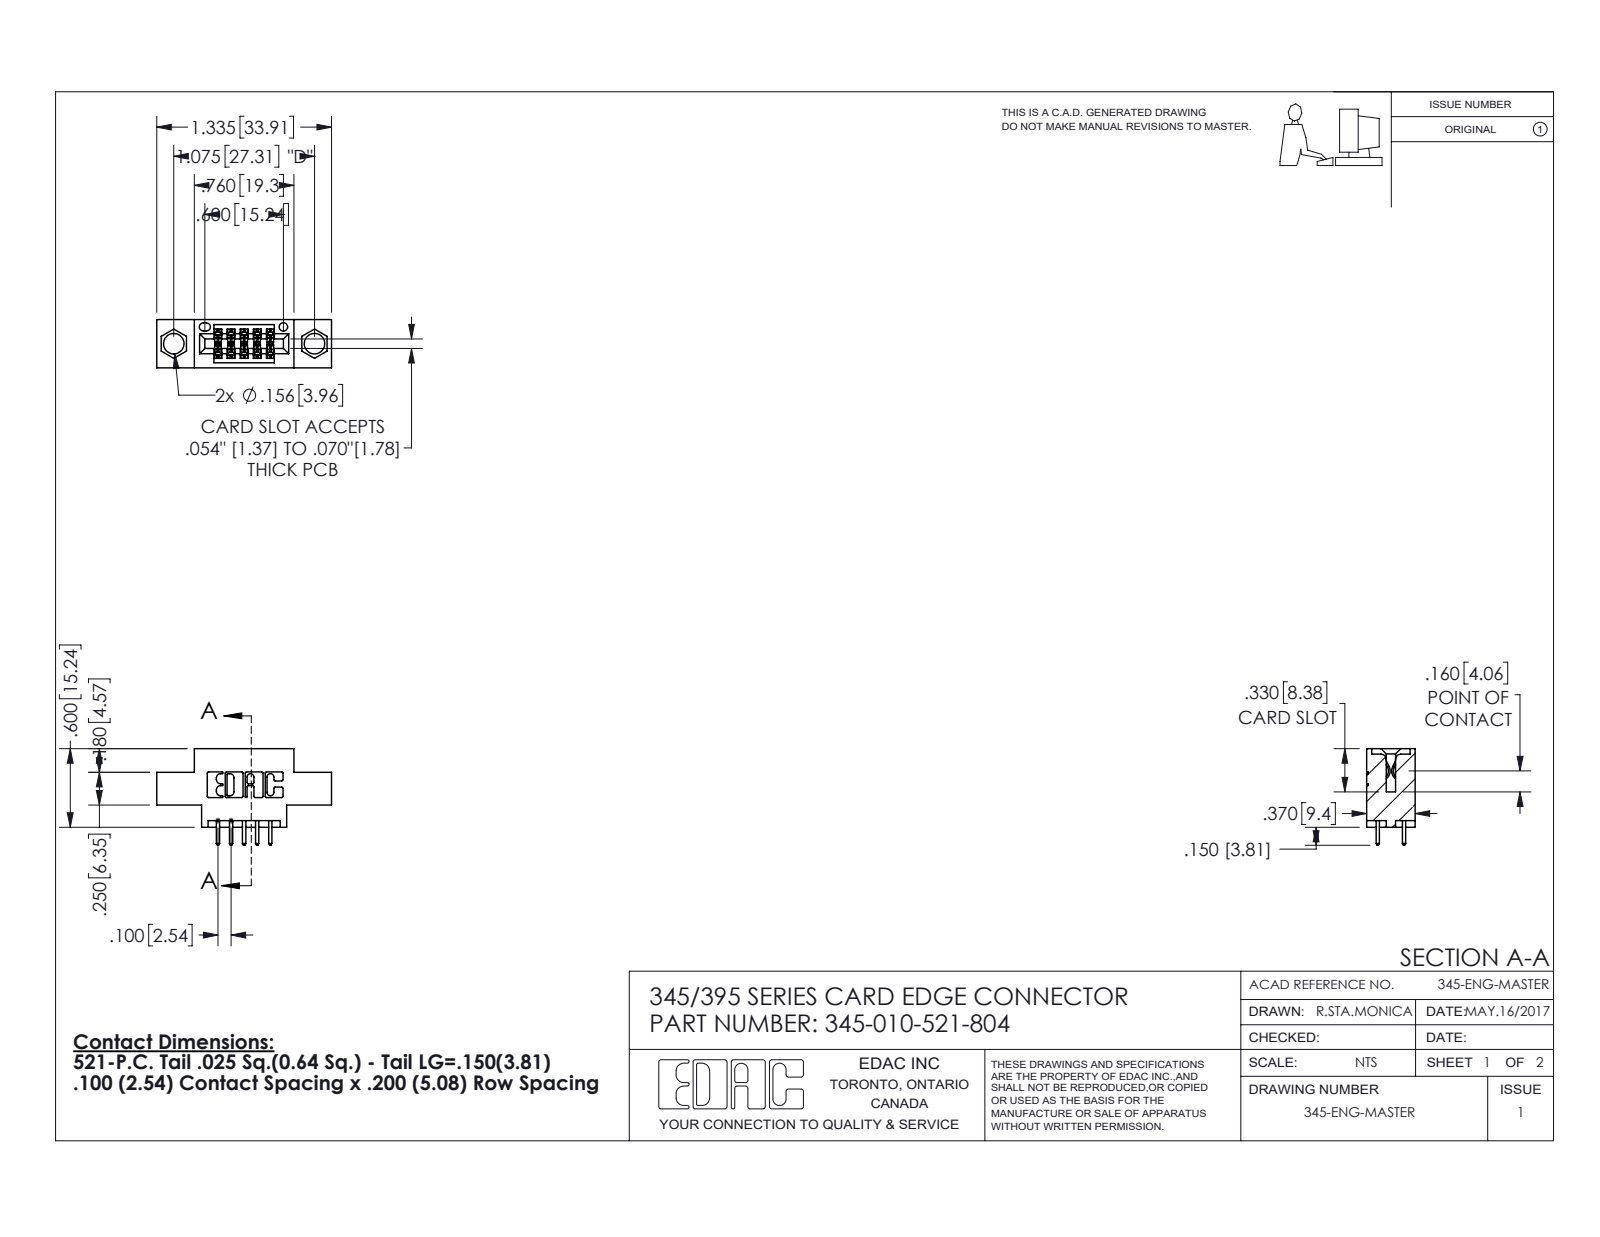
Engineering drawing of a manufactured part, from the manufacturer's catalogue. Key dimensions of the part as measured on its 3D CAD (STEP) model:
Part name (STEP PRODUCT): 345-010-521-804; 345 Part_0.170 Offset - 0.156 Dia-TI; 345-292-001_345-293-121
STEP written by: SolidWorks 2020 (CONFIG_CONTROL_DESIGN)
Units: inches
Bodies: 11 solids, 644 faces (428 planar, 216 cylindrical, 0 other)
Overall size (bounding box): 1.335 × 0.737 × 0.37
Volume: 0.166 in³ · Surface area: 5.089 in²
Round holes (diameter × count): ⌀0.156 ×2, ⌀0.064 ×1
Partial cylindrical surfaces — rounded edges, fillets, slot ends (radius × count): R0.01 ×22, R0.006 ×20, R0.01 ×10, R0.007 ×6, R0.031 ×6, R0.026 ×3, R0.014 ×2, R0.019 ×2
Main face-to-face distances: 0.37, 0.2, 0.072, 0.298, 0.1, 0.025, 0.098, 0.272, 0.25, 0.225
Hole centre spacings: 0.27, 0.847, 1.075
